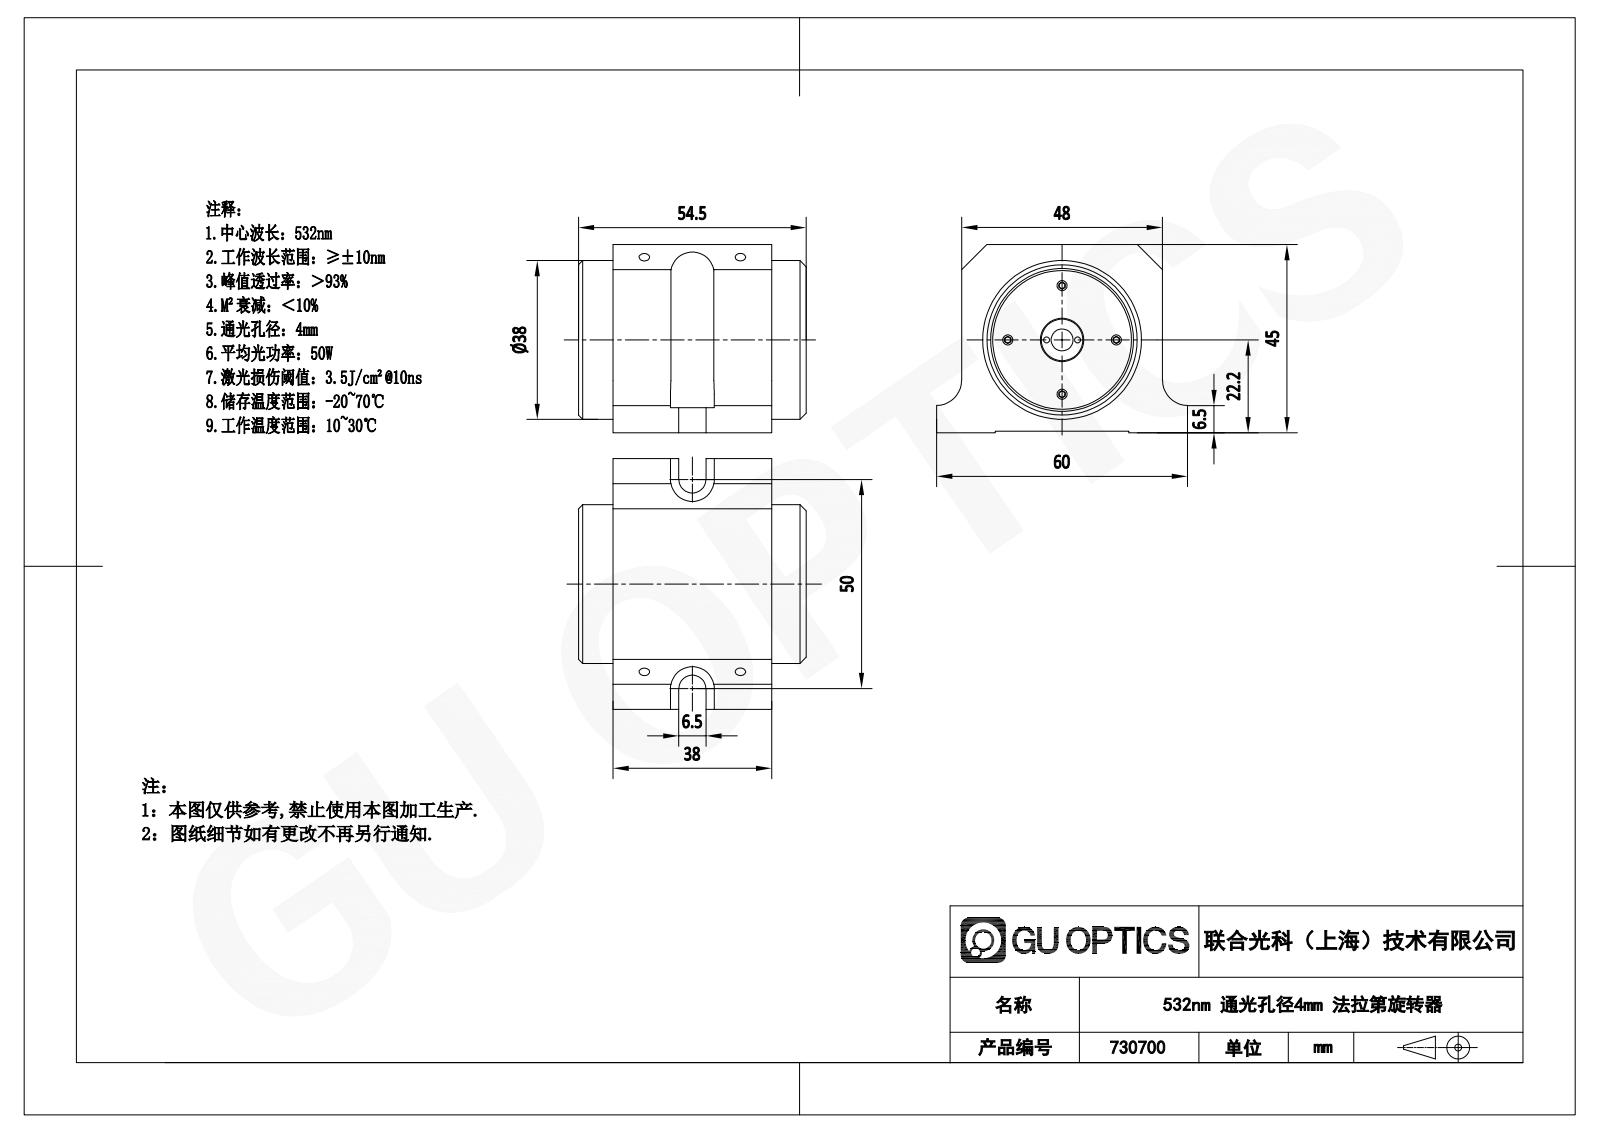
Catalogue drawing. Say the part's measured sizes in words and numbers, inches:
The part is named "730701". Its 3-D file was written by "SolidWorks 2020 (CONFIG_CONTROL_DESIGN)". It is 1 solid with 250 faces: 153 planar, 62 cylindrical and 35 other. Overall it measures 2.362 by 2.146 by 1.772 inches. Its volume is 3.692 cubic inches and its surface area 34.54 square inches. Round holes: 6 of diameter 0.098, 4 of diameter 0.063, 3 of diameter 0.087, 2 of diameter 0.059, 2 of diameter 0.118, 1 of diameter 0.209, 1 of diameter 0.315, 1 of diameter 0.787, 1 of diameter 0.807, 1 of diameter 0.866, 1 of diameter 1.299, 1 of diameter 1.307. Round bosses or shafts: 4 of diameter 0.071, 3 of diameter 0.15, 3 of diameter 0.079, 3 of diameter 0.076, 1 of diameter 1.496, 1 of diameter 1.339, 1 of diameter 0.394. Partial cylindrical surfaces (rounded edges, fillets, slot ends): 2 of radius 0.128, 2 of radius 0.207, 2 of radius 0.236. The main face-to-face distances are 0.016, 1.772, 1.756, 1.496, 0.325, 1.821, 0.236, 0.089, 1.585, 1.89. The hole center spacings are 0.256, 0.572, 0.512, 0.532, 0.294, 0.362, 0.724, 0.768.
